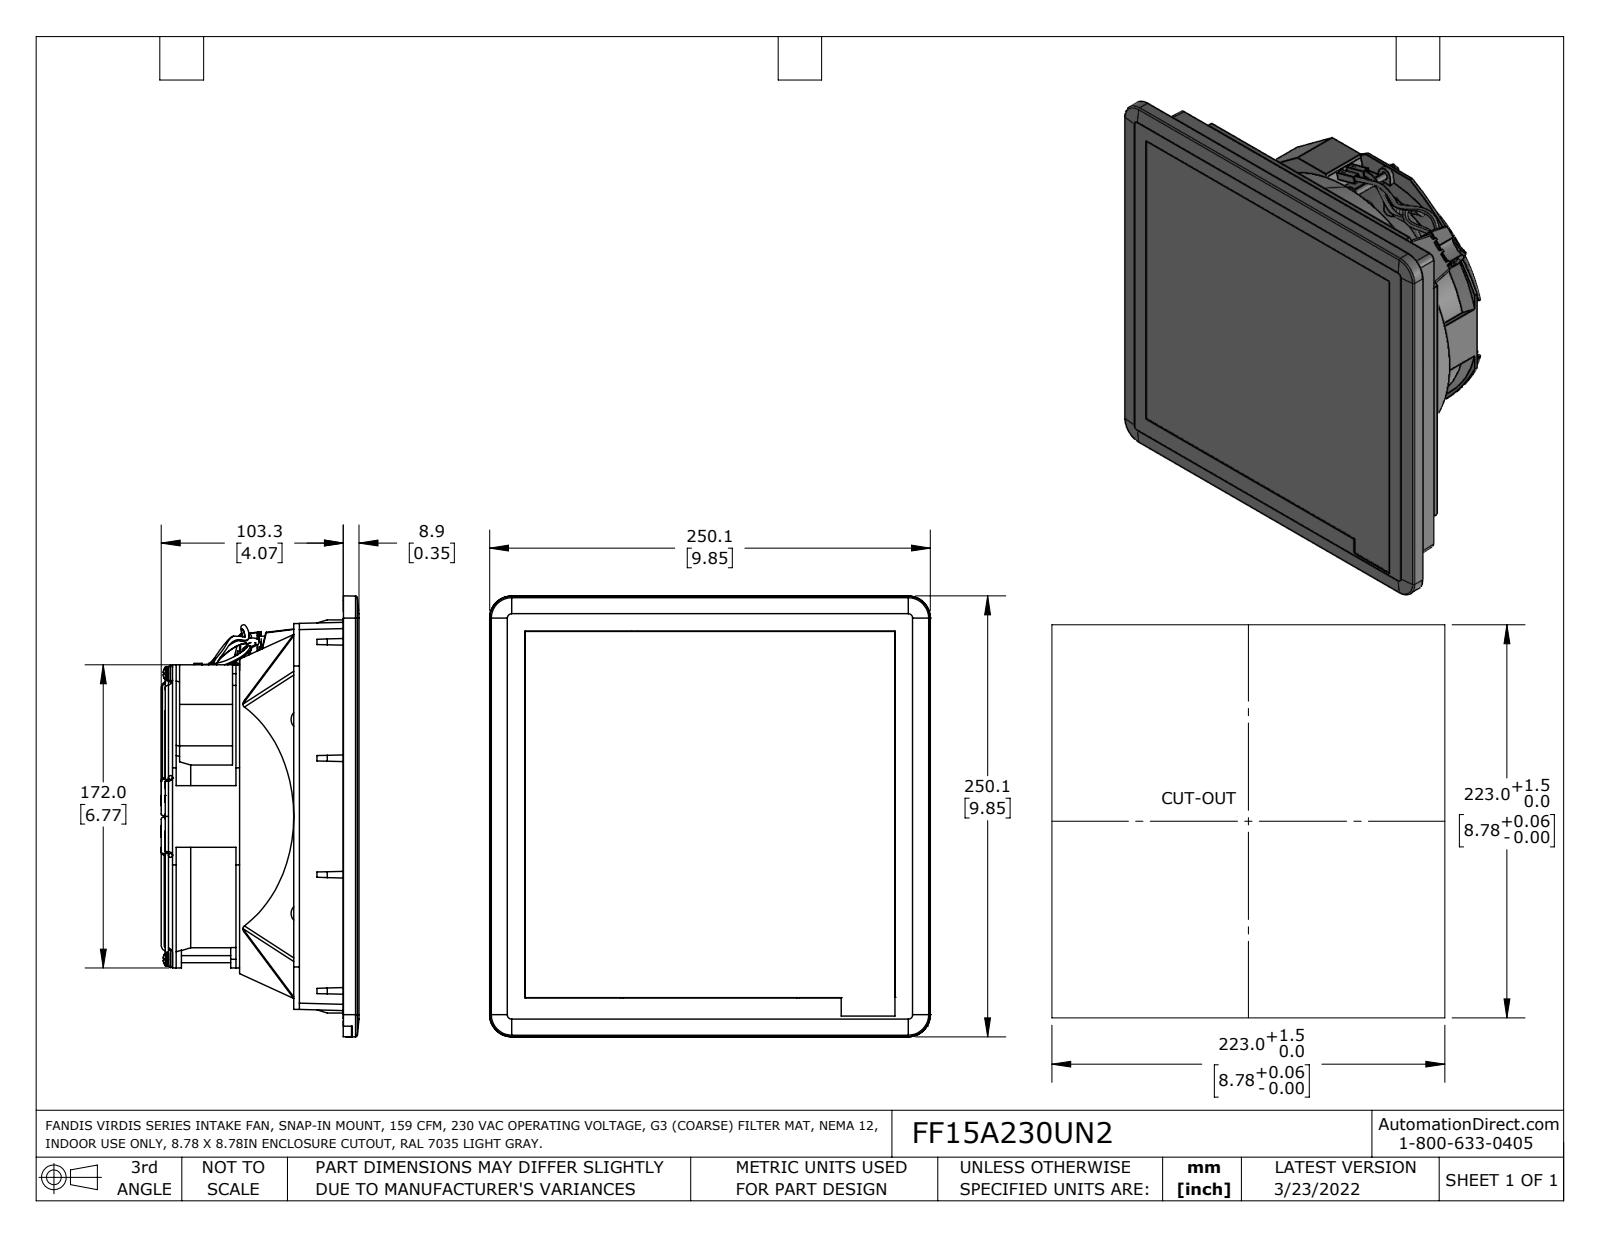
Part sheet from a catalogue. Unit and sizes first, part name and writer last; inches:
Units: inches
Overall size (bounding box): 9.847 × 9.847 × 4.418
Round holes (diameter × count): ⌀0.197 ×2, ⌀0.039 ×1, ⌀0.138 ×1, ⌀0.173 ×1
Round bosses / shafts (diameter × count): ⌀0.315 ×2, ⌀0.157 ×2, ⌀0.13 ×2, ⌀5.866 ×1, ⌀0.354 ×1, ⌀0.039 ×1
Partial cylindrical surfaces — rounded edges, fillets, slot ends (radius × count): R0.012 ×33, R0.02 ×19, R0.016 ×15, R0.039 ×13, R0.028 ×11, R0.197 ×10, R0.031 ×8, R0.051 ×8
Main face-to-face distances: 4.146, 0.331, 3.815, 0.02, 0.35, 4.165, 0.079, 1.437, 1.417, 1.339
Hole centre spacings: 0.646, 6.378, 6.441
Volume: 219.4 in³ · Surface area: 364.7 in²
Bodies: 26 solids, 1099 faces (585 planar, 287 cylindrical, 227 other)
Part name (STEP PRODUCT): FF15A230UN2
STEP written by: SolidWorks 2021 (AUTOMOTIVE_DESIGN)
